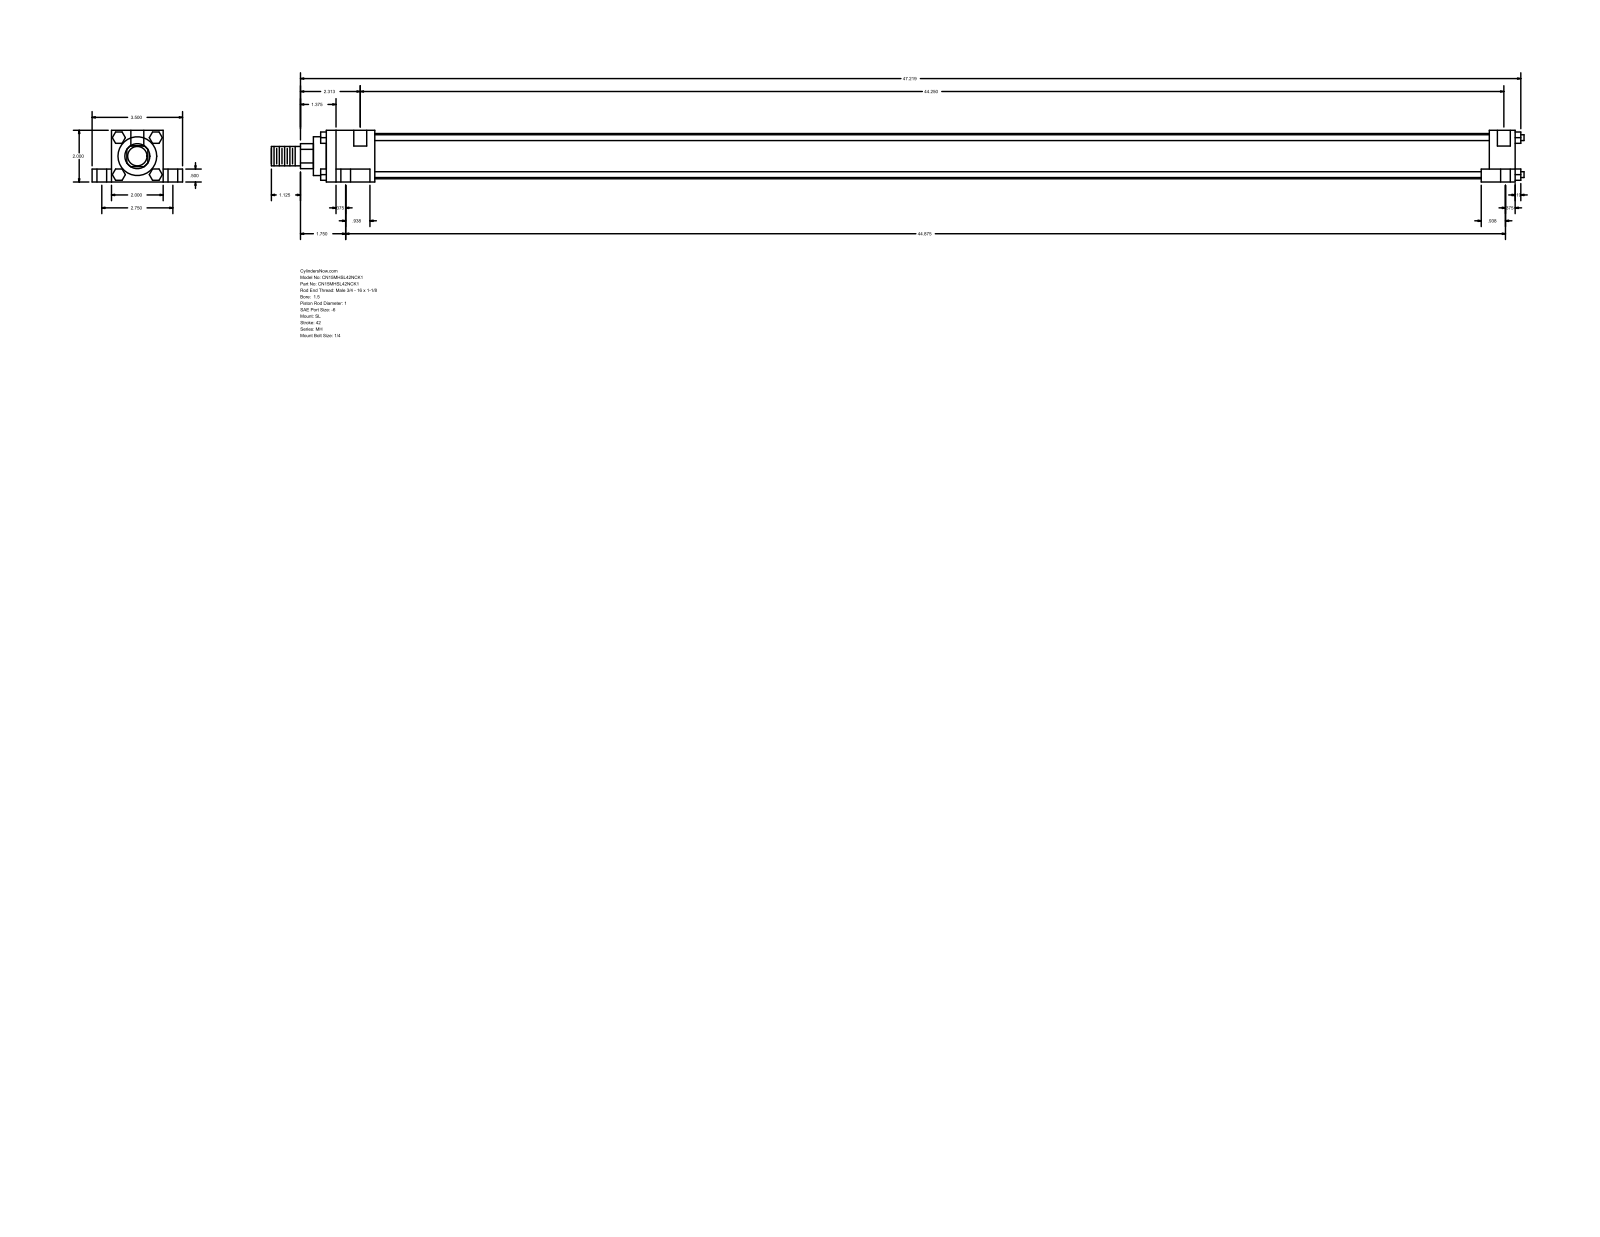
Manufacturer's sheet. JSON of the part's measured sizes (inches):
{"part_name": "MH_SL__0150_1", "step_written_by": "GSSL Pune (CONFIG_CONTROL_DESIGN)", "units": "inches", "bodies": {"solids": 0, "faces": 148, "planar": 112, "cylindrical": 36, "other": 0}, "overall_size": [48.469, 3.5, 2], "round_holes": [[0.219, 4], [0.375, 4], [0.625, 4], [0.5, 2]], "round_bosses_or_shafts": [[0.225, 4], [1.75, 1], [1.5, 1], [1, 1], [0.75, 1]], "partial_cylinders_radius": [[0.484, 1]], "face_to_face_distances": [2, 0.5, 1.5, 0.75, 2.75, 46, 1, 0.375, 1.313, 44.313], "hole_center_spacings": [1.376, 1.443, 1.485, 2.75, 44.334, 44.375, 44.459, 44.834]}
